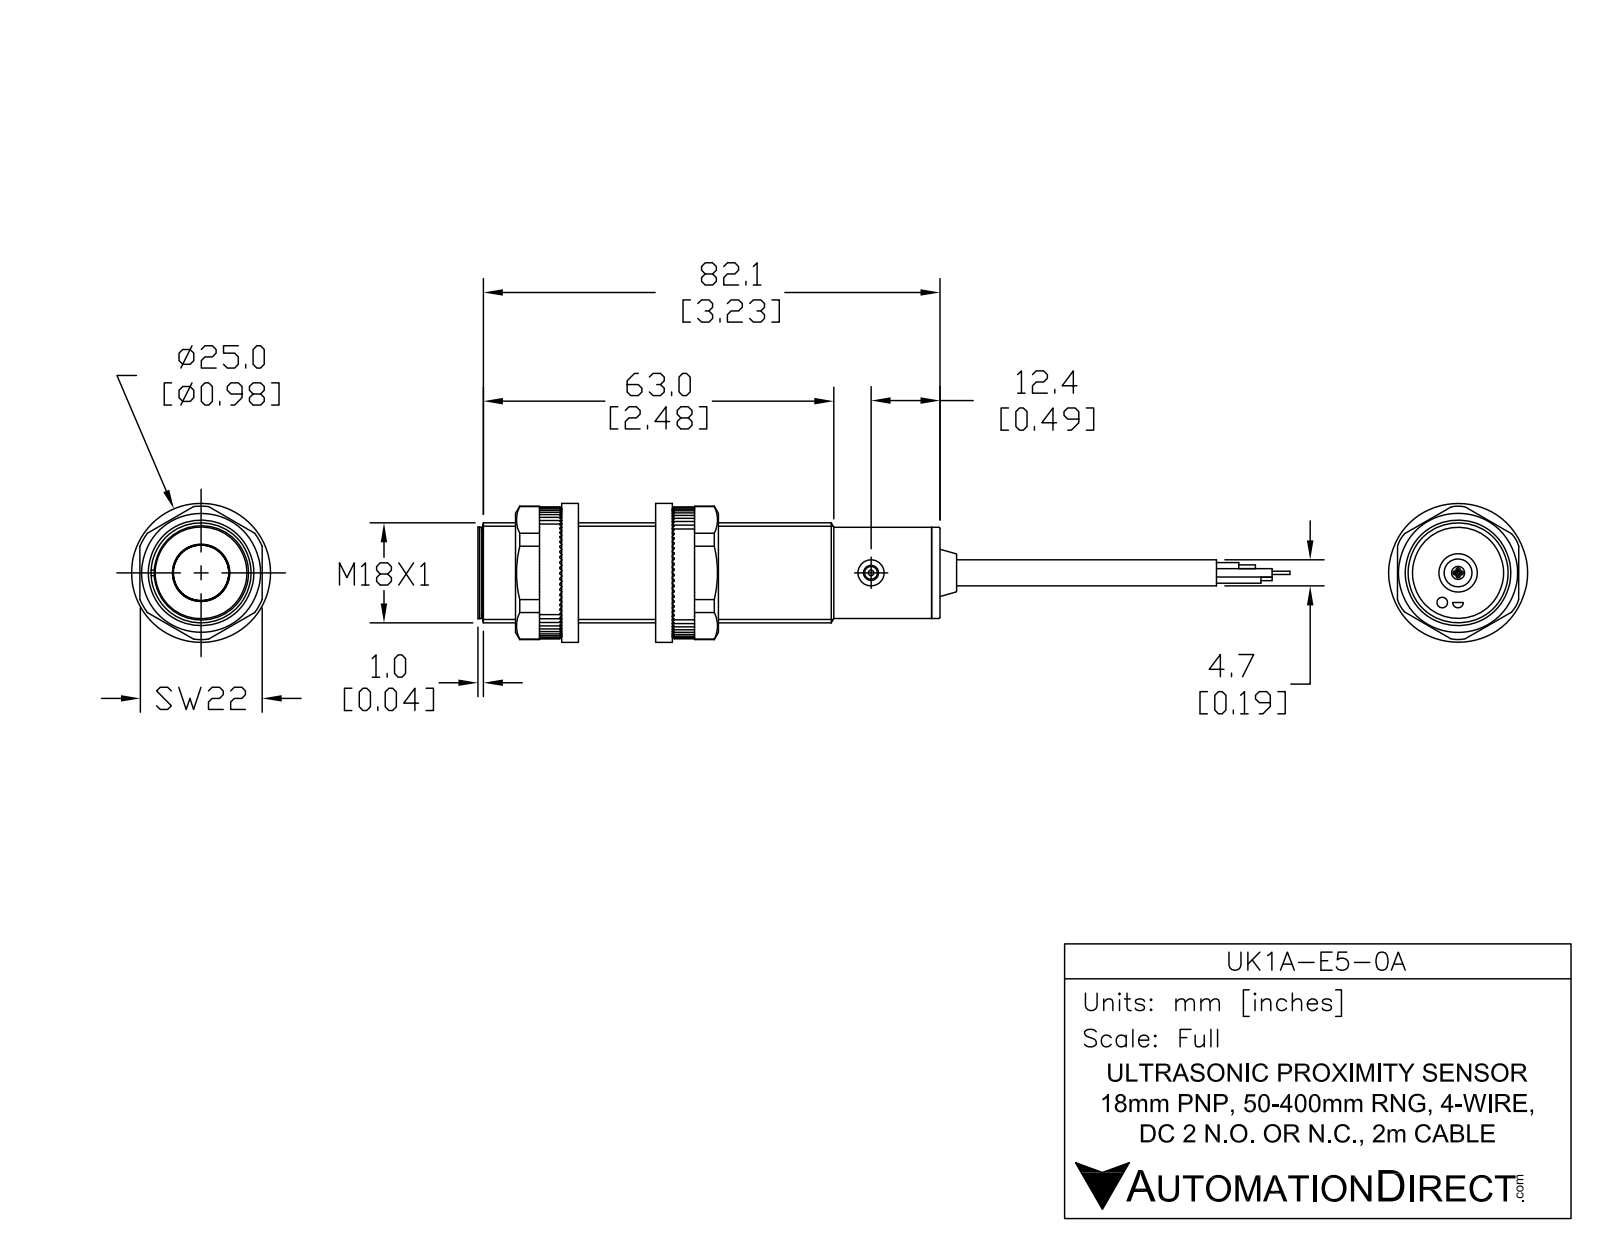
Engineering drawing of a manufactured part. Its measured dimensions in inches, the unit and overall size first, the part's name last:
Units: inches
Overall size (bounding box): 4.832 × 0.709 × 0.709
Round holes (diameter × count): ⌀0.185 ×2, ⌀0.106 ×1
Round bosses / shafts (diameter × count): ⌀0.709 ×1, ⌀0.646 ×1, ⌀0.622 ×1, ⌀0.374 ×1, ⌀0.189 ×1, ⌀0.091 ×1
Main face-to-face distances: 3.193, 3.252, 0.059, 0.039, 3.232, 3.291, 0.041, 3.234, 3.293, 3.257
Volume: 1.285 in³ · Surface area: 10.69 in²
Bodies: 6 solids, 55 faces (17 planar, 24 cylindrical, 14 other)
Part name (STEP PRODUCT): UK1A-E5-0A
STEP written by: SolidWorks 2017 (AUTOMOTIVE_DESIGN)
